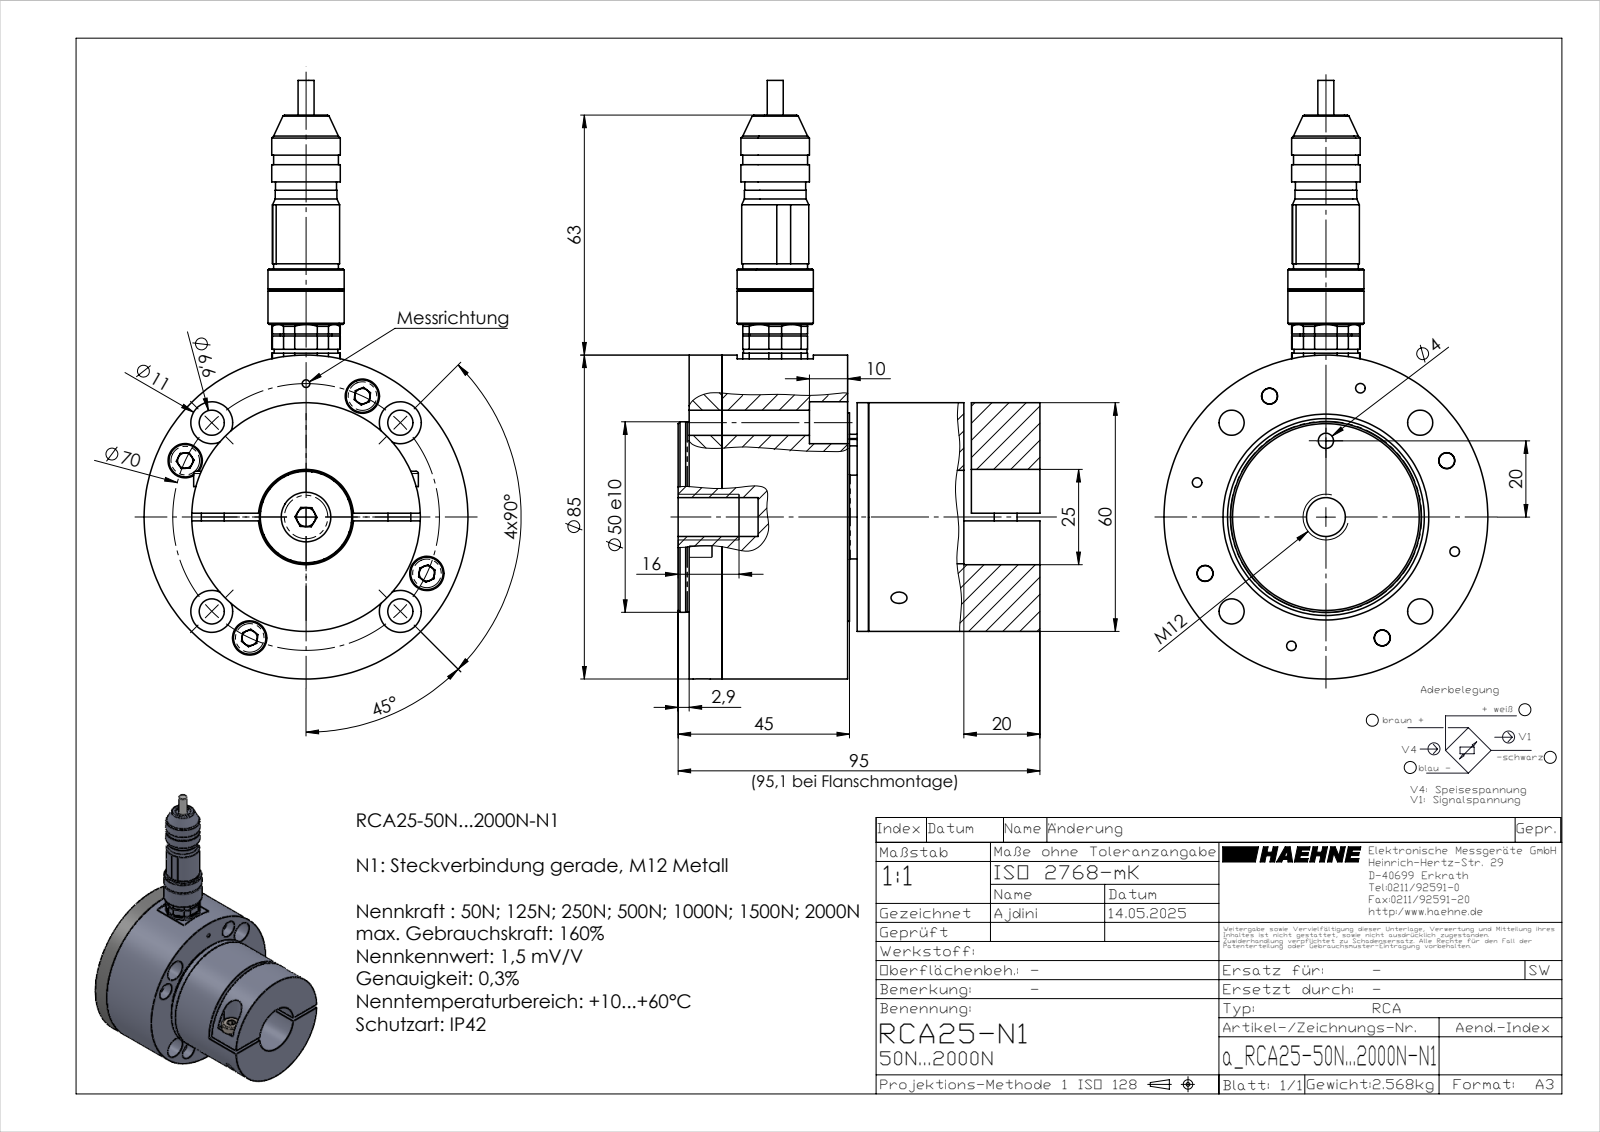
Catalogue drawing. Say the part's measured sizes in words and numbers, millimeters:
The part is named "inafag_1203-tvh_7zkvytp7yxkimpdvw8sj0b5w4_14; Y02043Z1 inafag_1203-tvh_7zkvytp7yxkimpdvw8sj0b5w4; a_RC-N2 Flanschmontage Scheibe; inafag_1203-tvh_7zkvytp7yxkimpdvw8sj0b5w4_04 (+8 more)". Its 3-D file was written by "SolidWorks 2023 (AUTOMOTIVE_DESIGN)". It is 54 solids with 743 faces: 377 planar, 203 cylindrical and 163 other. Overall it measures 157.06 by 95.1 by 85 millimeters. Its volume is 373 504 cubic millimeters and its surface area 114 133 square millimeters. Round holes: 9 of diameter 3.4, 8 of diameter 2.5, 6 of diameter 6.6, 5 of diameter 1, 5 of diameter 4.2, 4 of diameter 4, 4 of diameter 5.3, 4 of diameter 9, 4 of diameter 11, 2 of diameter 4.5, 2 of diameter 5, 1 of diameter 2. Round bosses or shafts: 9 of diameter 3, 8 of diameter 5.7, 4 of diameter 8.5, 4 of diameter 5, 4 of diameter 1.5, 4 of diameter 1, 2 of diameter 17, 2 of diameter 10. Partial cylindrical surfaces (rounded edges, fillets, slot ends): 6 of radius 0.3, 4 of radius 1, 2 of radius 5.5, 1 of radius 0.57, 1 of radius 0.6, 1 of radius 0.77, 1 of radius 3.5. The main face-to-face distances are 3, 2, 8.6, 47.1, 45, 11.6, 50, 30, 35.5, 38.5. The hole center spacings are 35, 49.5, 24.78, 25.2, 32.8, 51.14, 56.46, 2.5.
